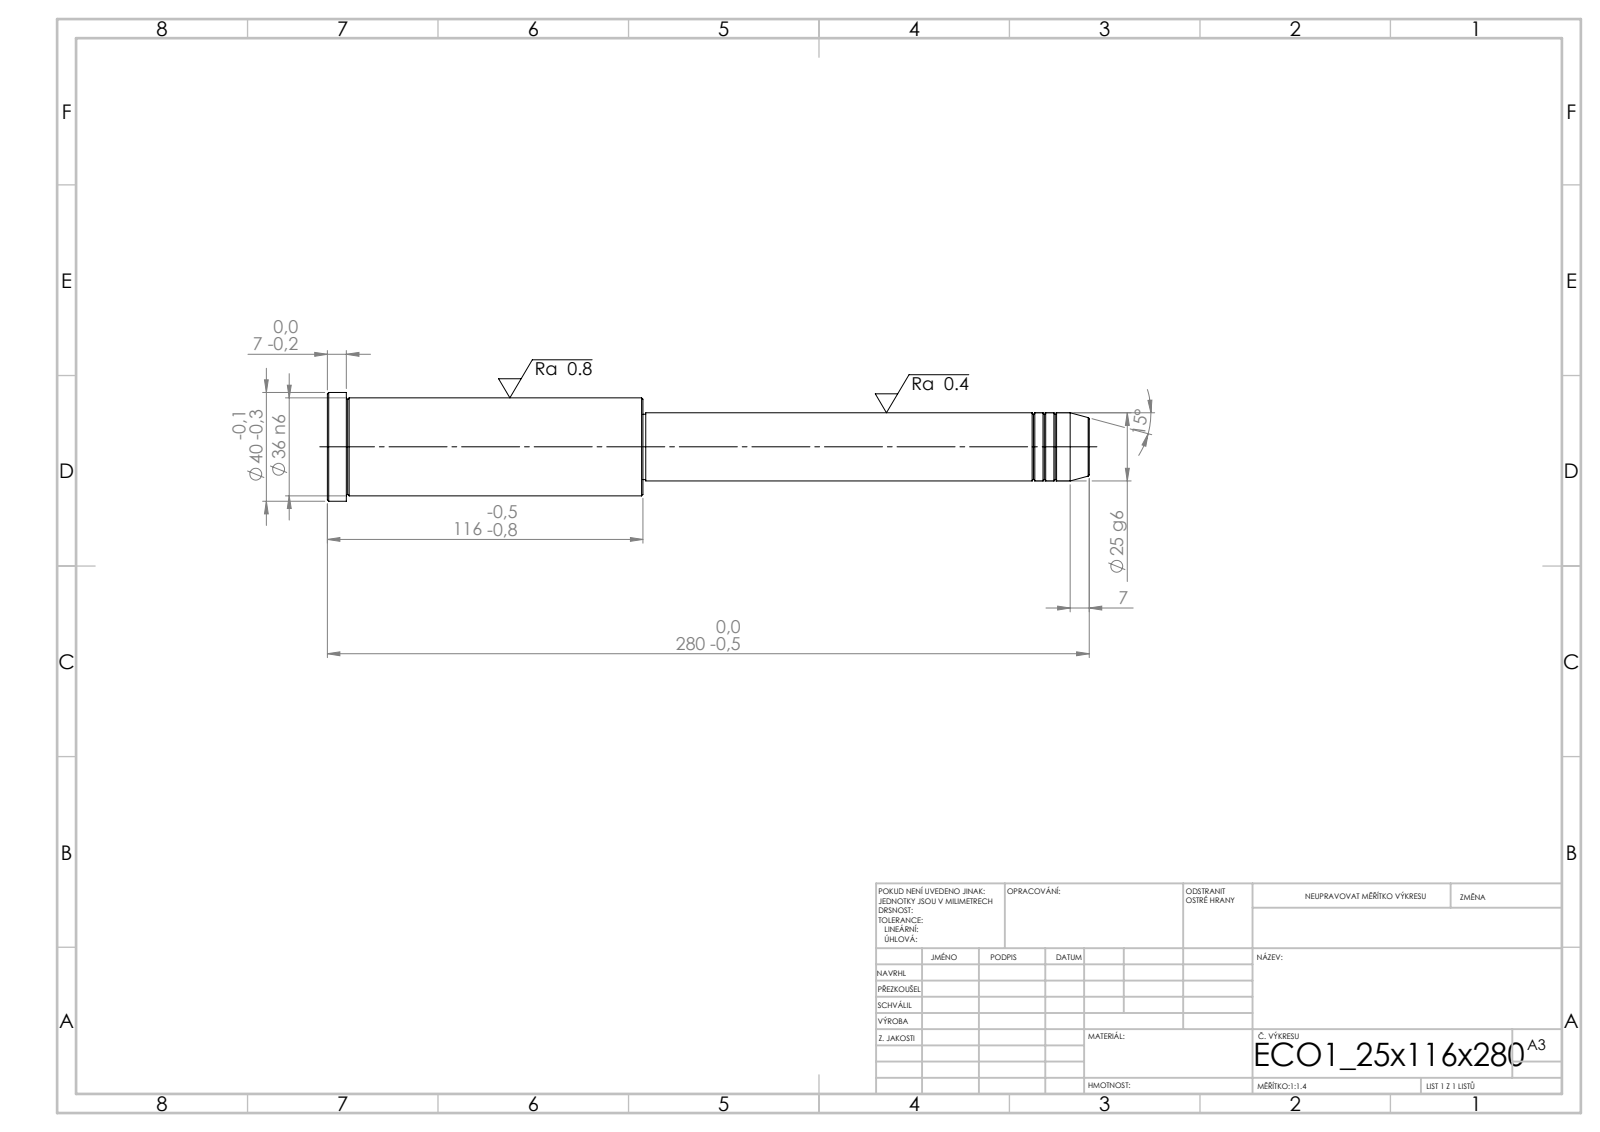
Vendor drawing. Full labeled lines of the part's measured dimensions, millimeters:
STEP written by: SolidWorks 2019 (CONFIG_CONTROL_DESIGN)
Units: millimetres
Bodies: 1 solid, 43 faces (5 planar, 14 cylindrical, 24 other)
Overall size (bounding box): 280 × 40 × 40
Volume: 199 554 mm³ · Surface area: 28 624 mm²
Round bosses / shafts (diameter × count): ⌀40 ×1, ⌀36 ×1, ⌀25 ×1, ⌀24 ×1
Main face-to-face distances: 116, 164, 280, 273, 109, 7, 163, 1, 110, 117
